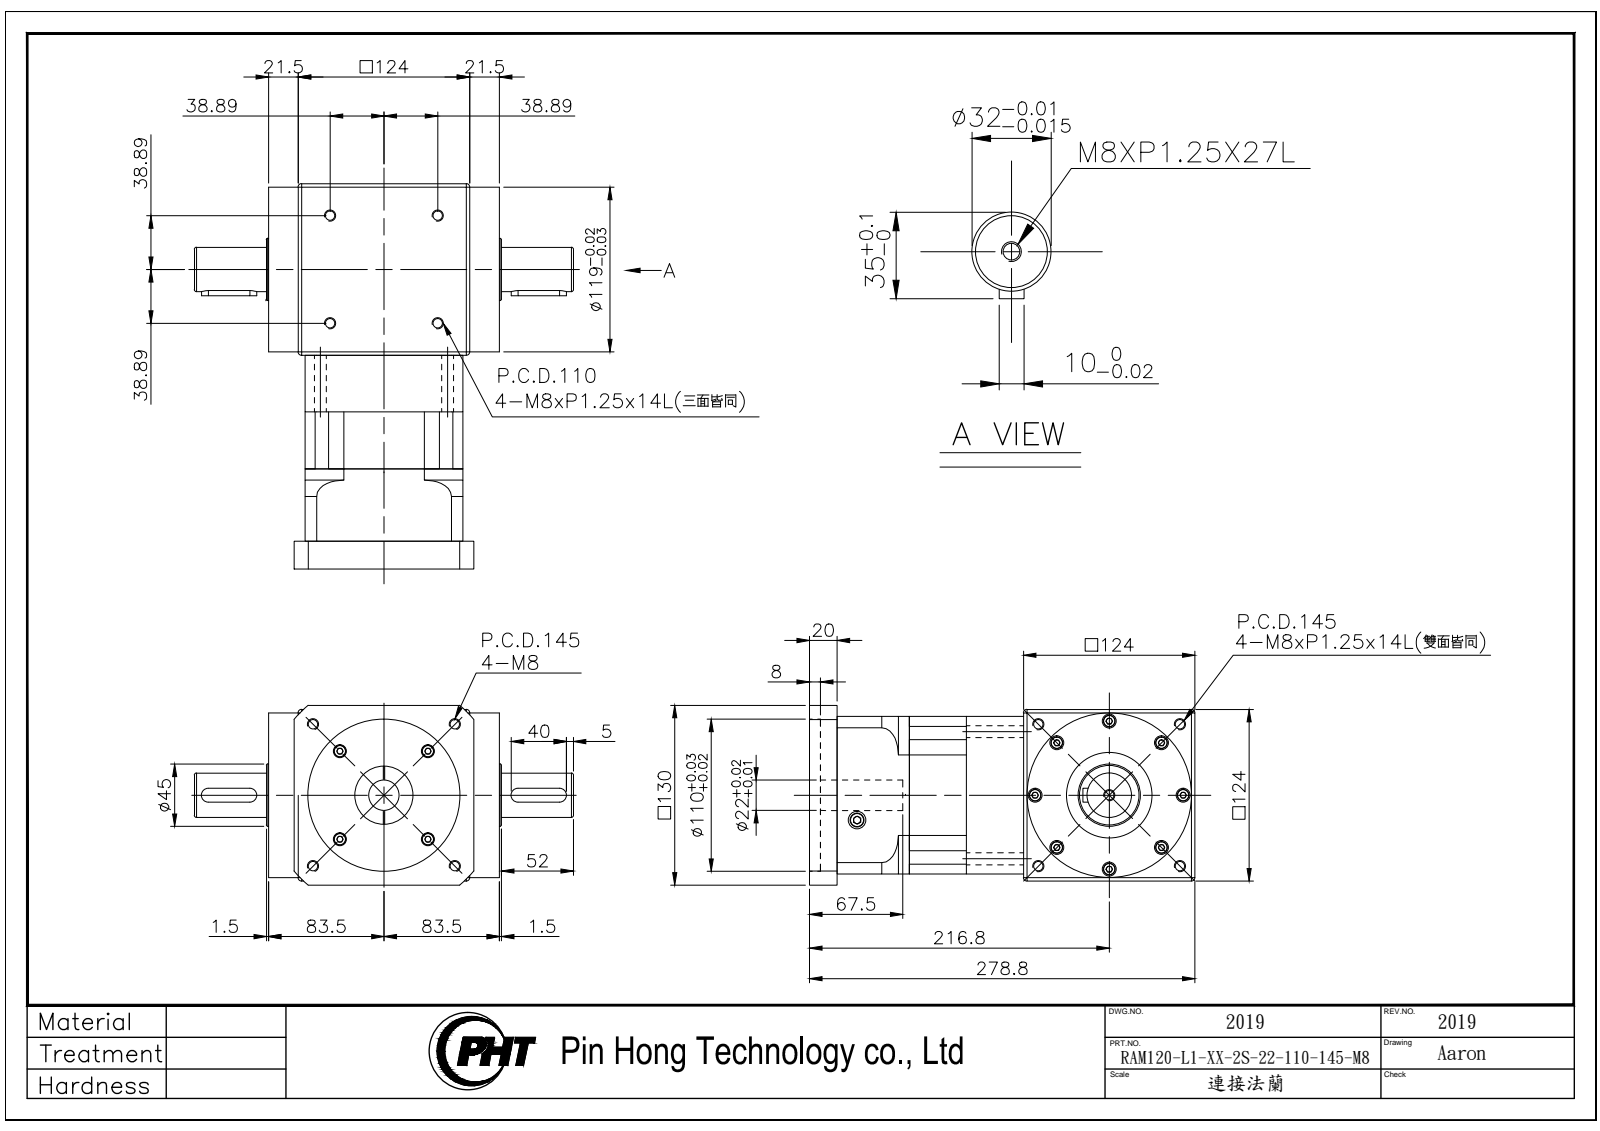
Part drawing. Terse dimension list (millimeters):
name: RAM120-L1-XX-2S-22-110-145-M8_2019
written by: SolidWorks 2016 (AUTOMOTIVE_DESIGN)
unit: mm
bodies: 6 solids, 994 faces (490 planar, 324 cylindrical, 180 other)
size: 278.8 × 274 × 130
volume: 4 256 000 mm³; area: 354 338 mm²
holes: 17× ⌀6.8, 12× ⌀9.5, 8× ⌀5.3, 8× ⌀9, 8× ⌀14, 4× ⌀4.2, 4× ⌀5.5, 4× ⌀8.6, 2× ⌀12.7, 1× ⌀4.08, 1× ⌀22, 1× ⌀42
bosses: 12× ⌀13, 12× ⌀8.5, 1× ⌀119, 1× ⌀62, 1× ⌀49, 1× ⌀45, 1× ⌀32
rounds: 4× R5, 4× R7, 1× R64, 1× R75, 1× R85, 1× R86.2
face distances: 124, 5, 119, 41.5, 114, 3, 41, 82.5, 8, 206.5
hole spacings: 59, 10, 15.4, 17.24, 19.42, 21.77, 39.8, 51.28
